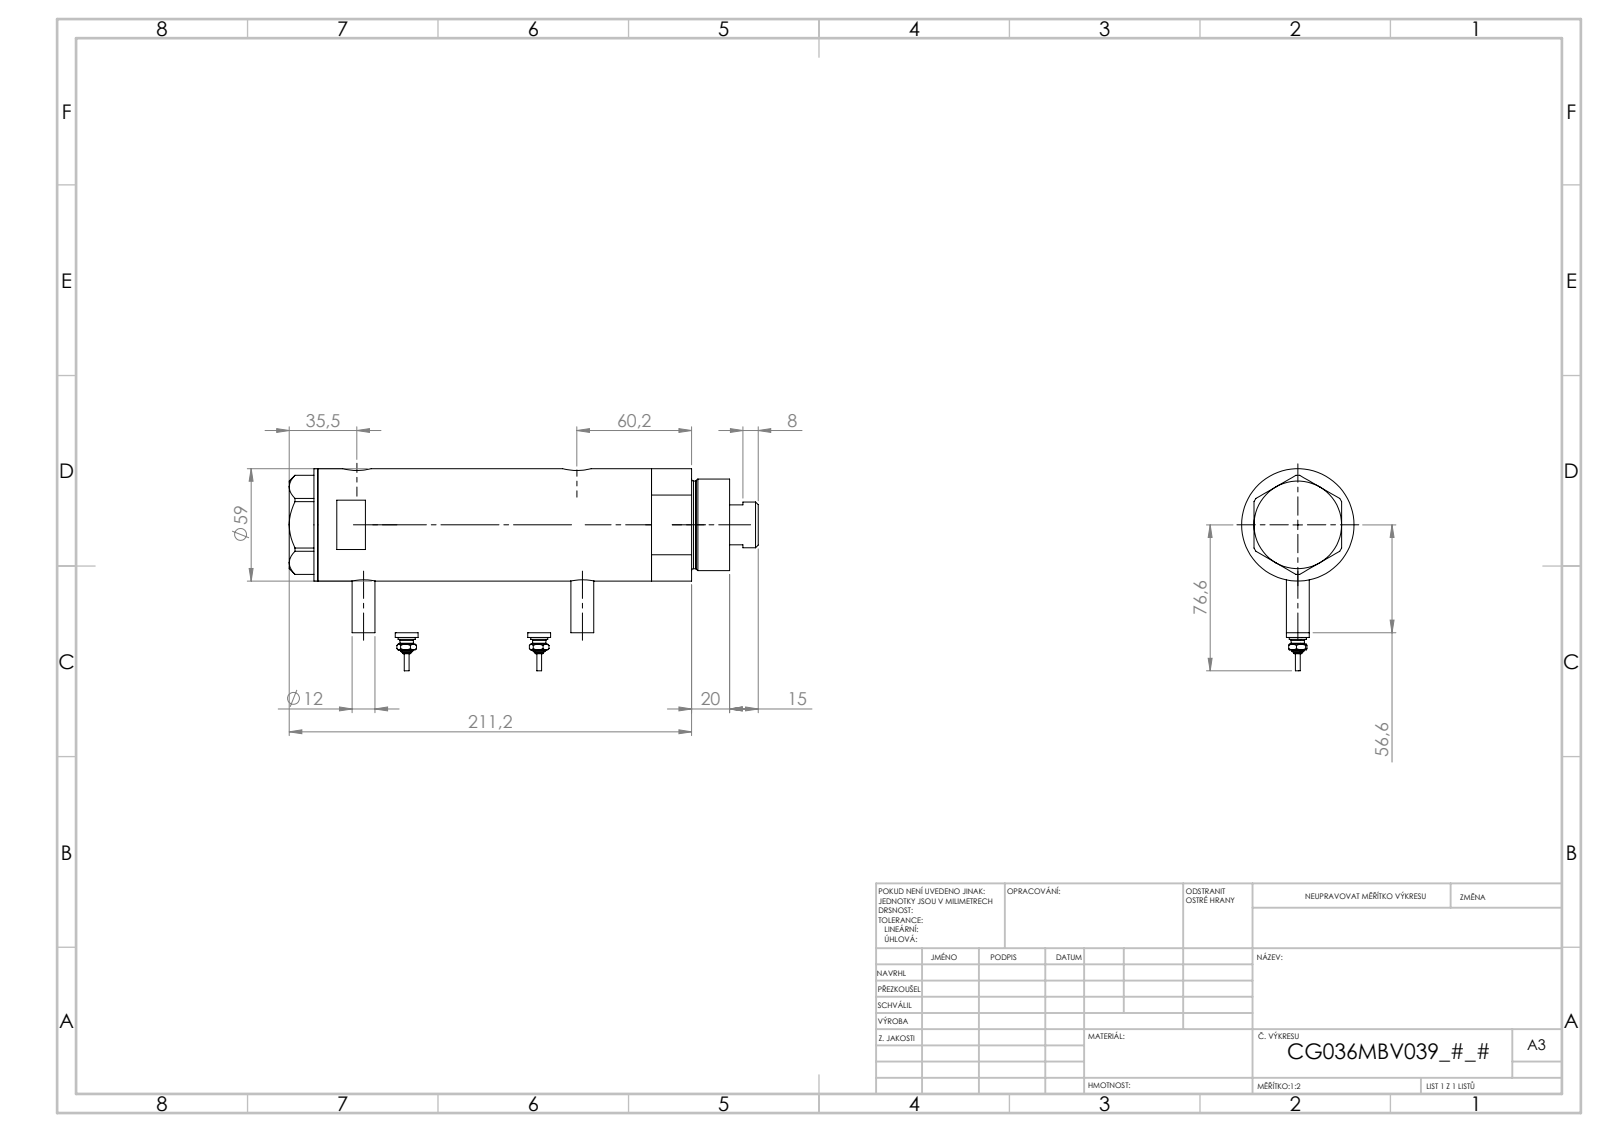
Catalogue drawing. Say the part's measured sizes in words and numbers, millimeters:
The part is named "Switch; V270CG_FRONT; V270CG_VC; V270CG_BACK (+1 more)". Its 3-D file was written by "SolidWorks 2019 (CONFIG_CONTROL_DESIGN)". It is 6 solids with 212 faces: 79 planar, 69 cylindrical and 64 other. Overall it measures 246.2 by 106.1 by 59 millimeters. Its volume is 585 944 cubic millimeters and its surface area 117 538 square millimeters. Round holes: 2 of diameter 9.73, 2 of diameter 12.5, 2 of diameter 15, 1 of diameter 8.5, 1 of diameter 25, 1 of diameter 26.5, 1 of diameter 36, 1 of diameter 40, 1 of diameter 52. Round bosses or shafts: 4 of diameter 12, 2 of diameter 9, 2 of diameter 7, 2 of diameter 4.5, 2 of diameter 2.5, 1 of diameter 59, 1 of diameter 48, 1 of diameter 46. The main face-to-face distances are 137.2, 23.5, 113.7, 15, 38.5, 152.2, 2, 231.2, 216.2, 192.7. The hole center spacings are 2.9, 3.5, 112, 114.9, 115.5, 118.4.
